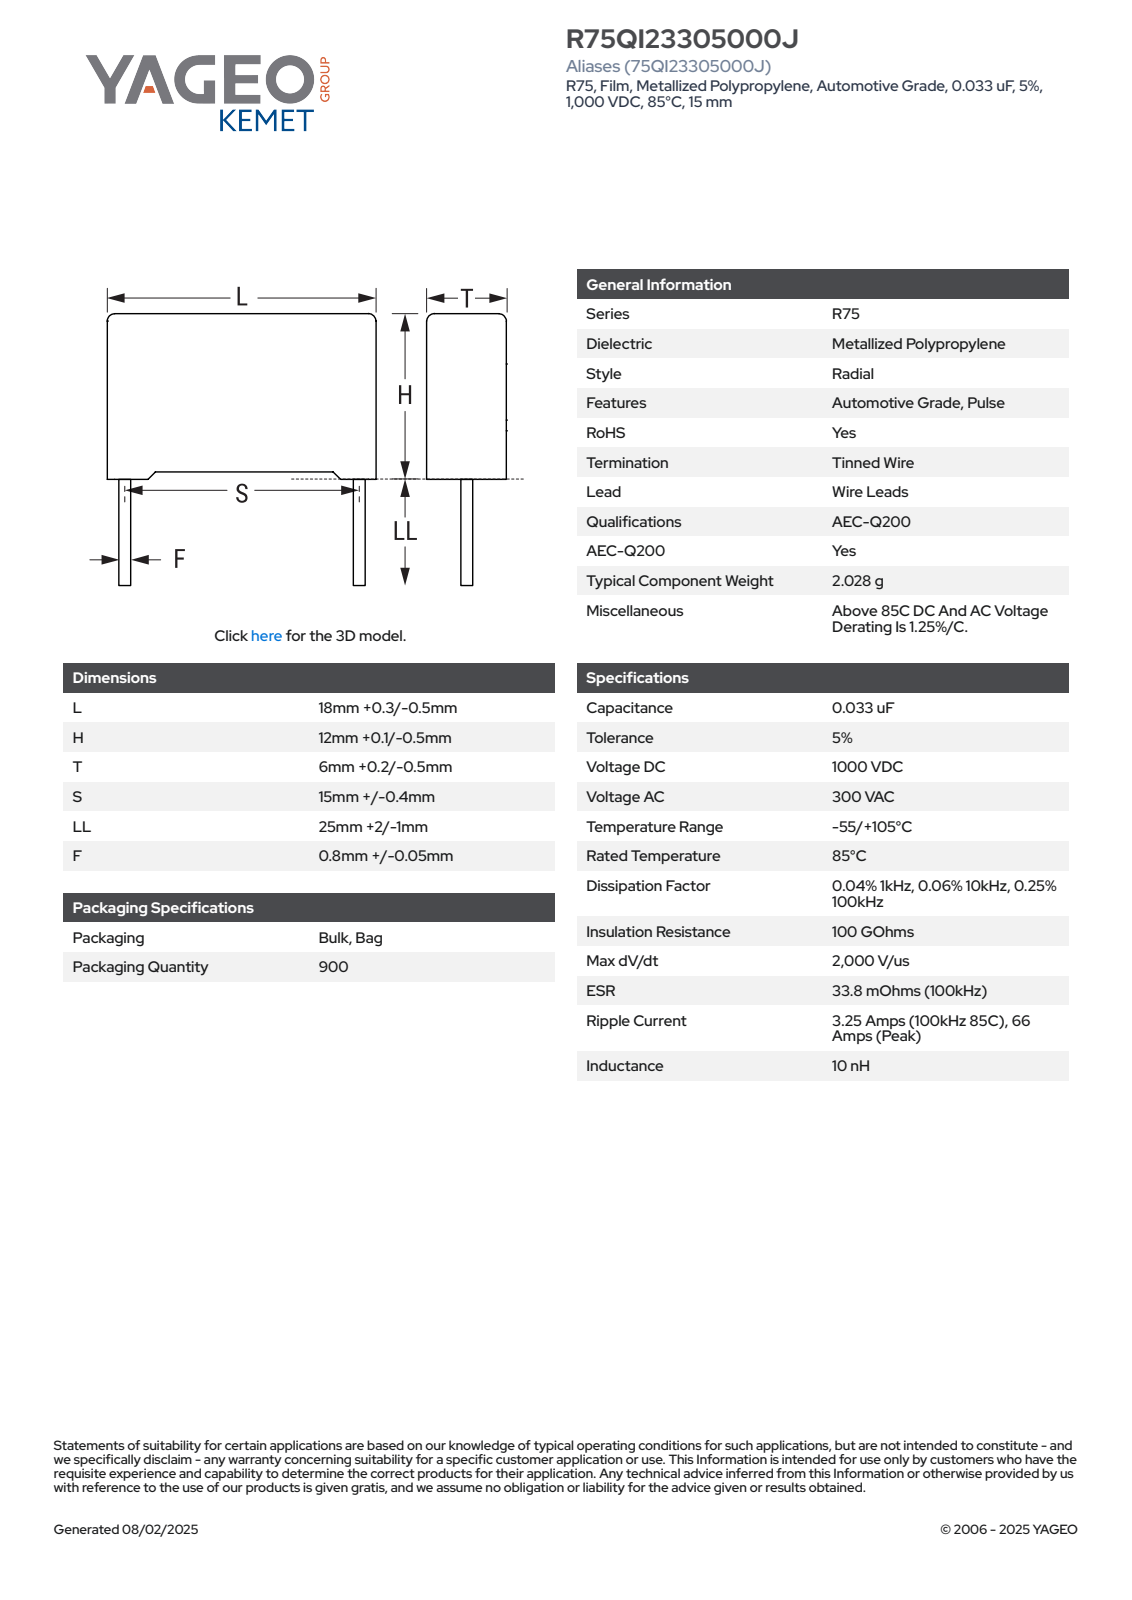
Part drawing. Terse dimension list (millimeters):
name: CFR_RB2_18X12X6_L18.3H12.1T6.2S15LL27F0.85
written by: SolidWorks 2021 (AUTOMOTIVE_DESIGN)
unit: mm
bodies: 4 solids, 85 faces (77 planar, 8 cylindrical, 0 other)
size: 39.1 × 18.3 × 6.21
volume: 1 332 mm³; area: 997 mm²
bosses: 2× ⌀0.85
rounds: 4× R0.5
face distances: 6.2, 11.35, 18.3, 0.61, 5.59, 0.75, 12.1, 0.42, 0.33, 11.68
